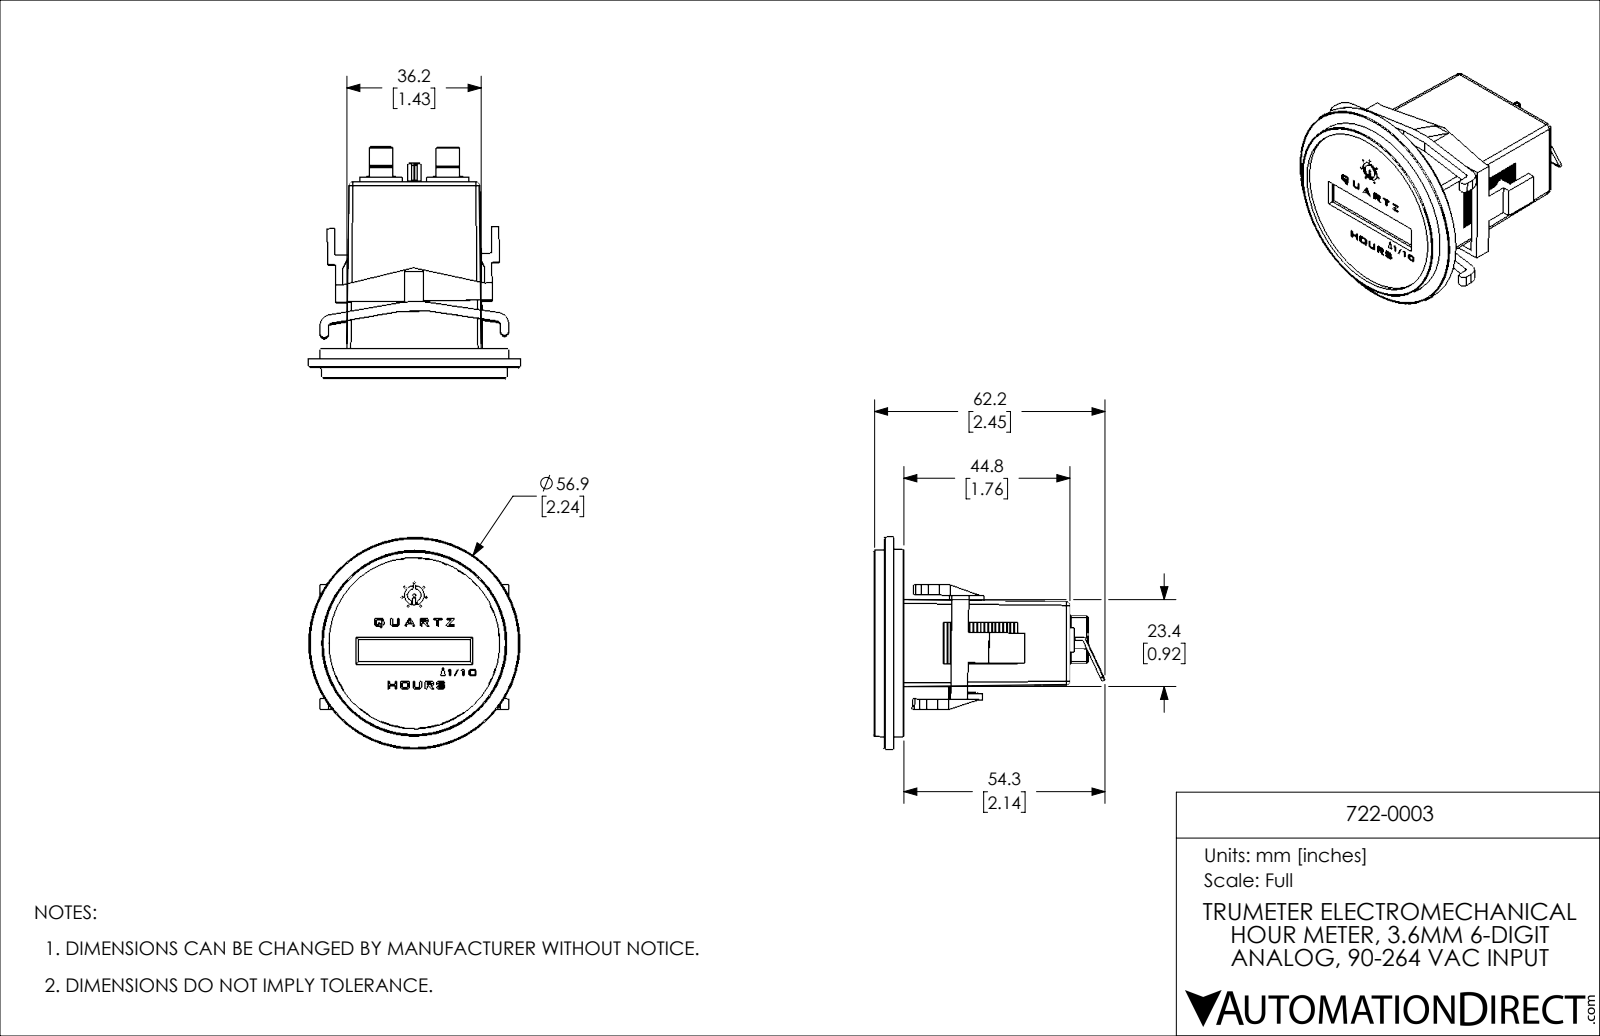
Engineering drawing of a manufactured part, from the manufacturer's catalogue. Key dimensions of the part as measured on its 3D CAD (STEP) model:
Part name (STEP PRODUCT): 722-0003
STEP written by: SolidWorks 2021 (CONFIG_CONTROL_DESIGN)
Units: millimetres
Bodies: 1 solid, 847 faces (640 planar, 147 cylindrical, 60 other)
Overall size (bounding box): 62.16 × 56.9 × 56.9
Volume: 18 935 mm³ · Surface area: 25 335 mm²
Round holes (diameter × count): ⌀0.5 ×7, ⌀1.5 ×4, ⌀0.84 ×1, ⌀5.26 ×1, ⌀46 ×1
Round bosses / shafts (diameter × count): ⌀50.3 ×1, ⌀3.58 ×1
Partial cylindrical surfaces — rounded edges, fillets, slot ends (radius × count): R0.5 ×30, R1 ×17, R0.3 ×15, R1.5 ×6, R0.35 ×4, R0.76 ×4, R1.15 ×4, R1.75 ×4
Main face-to-face distances: 1.4, 0.4, 2.5, 2.9, 4.3, 2.4, 1.8, 51.7, 50.3, 49.9
Hole centre spacings: 3.36, 2.85, 6.5, 5.16, 2.84, 3.37, 5.15, 5.51
